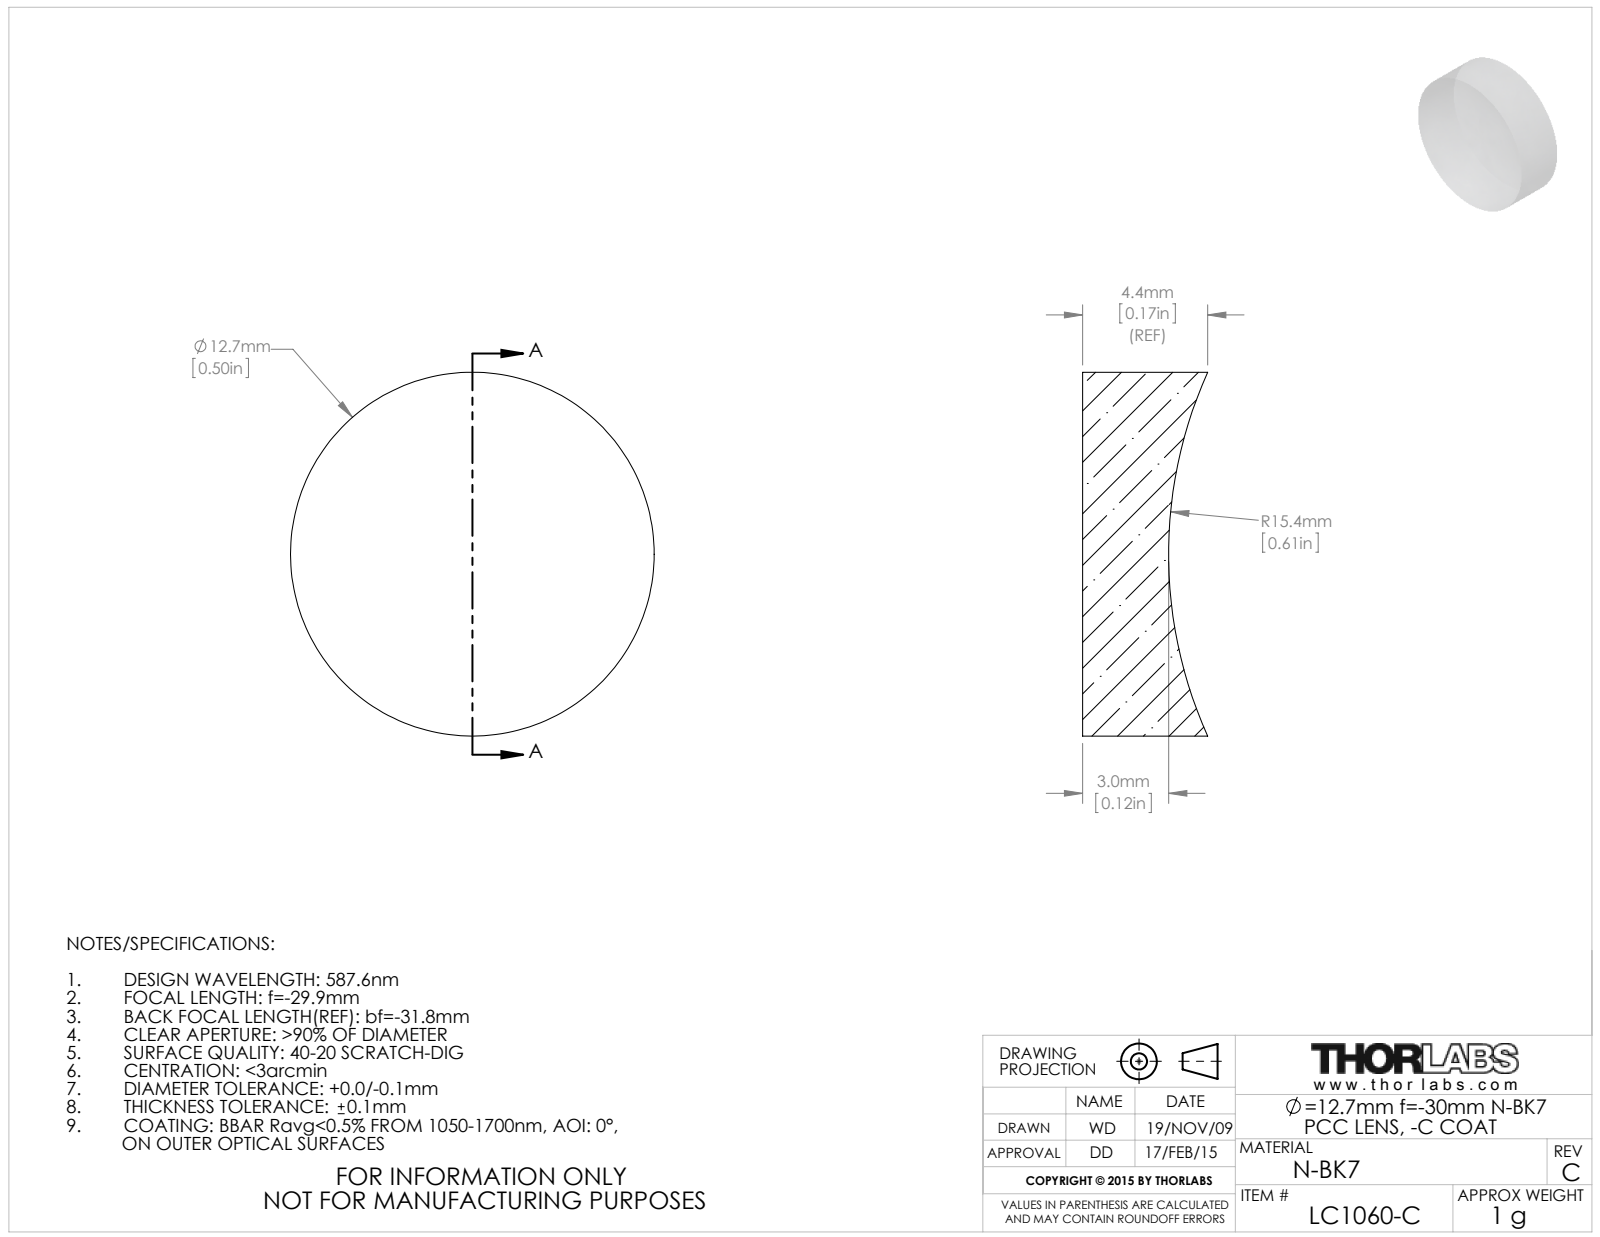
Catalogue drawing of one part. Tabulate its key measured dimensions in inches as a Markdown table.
| quantity | value |
| --- | --- |
| part name | 4802-E0W |
| STEP written by | SolidWorks 2009 (AUTOMOTIVE_DESIGN) |
| units | inches |
| bodies | 1 solid, 5 faces (1 planar, 2 cylindrical, 2 other) |
| overall size | 0.5 × 0.5 × 0.172 |
| volume | 0.028 in³ |
| surface area | 0.671 in² |
| round bosses / shafts (diameter × count) | 0.5 × 1 |
